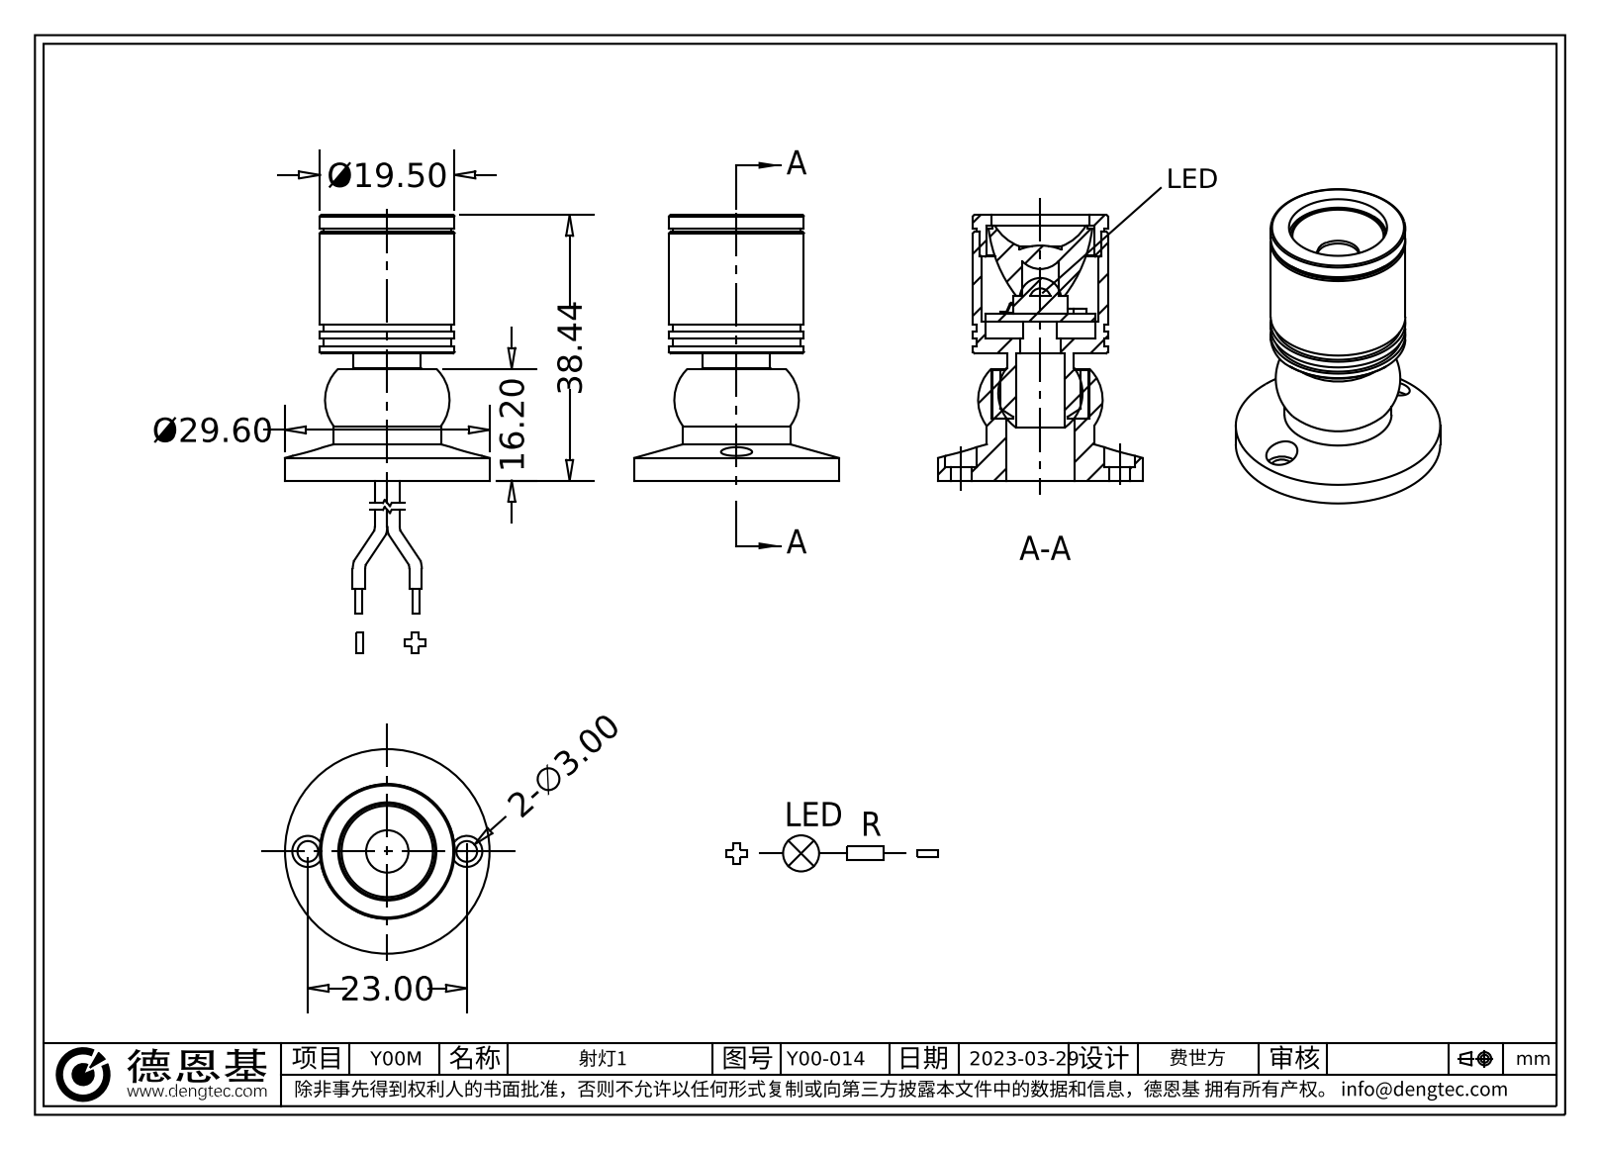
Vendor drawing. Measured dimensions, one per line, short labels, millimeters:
name: 透镜; ЙПёЗ; 射灯1; 橡胶圈 (+3 more)
written by: SolidWorks 2018 (CONFIG_CONTROL_DESIGN)
unit: mm
bodies: 10 solids, 228 faces (100 planar, 82 cylindrical, 46 other)
size: 38.44 × 29.6 × 29.6
volume: 8 172 mm³; area: 9 053 mm²
holes: 2× ⌀3, 2× ⌀4.5, 2× ⌀6, 1× ⌀5.2, 1× ⌀5.8, 1× ⌀6.13, 1× ⌀6.9, 1× ⌀7.9, 1× ⌀10, 1× ⌀11.6, 1× ⌀14.2, 1× ⌀15.5
bosses: 1× ⌀29.6, 1× ⌀19.5, 1× ⌀18.5, 1× ⌀14, 1× ⌀13.75, 1× ⌀9.72
rounds: 4× R0.3, 4× R1, 2× R0.1, 2× R0.5, 1× R4, 1× R8
face distances: 23.04, 24.24, 1.2, 18.44, 4.6, 5.8, 8.95, 9.49, 14.09, 15.29
hole spacings: 5, 6.5, 11.5, 16.5, 10, 23
